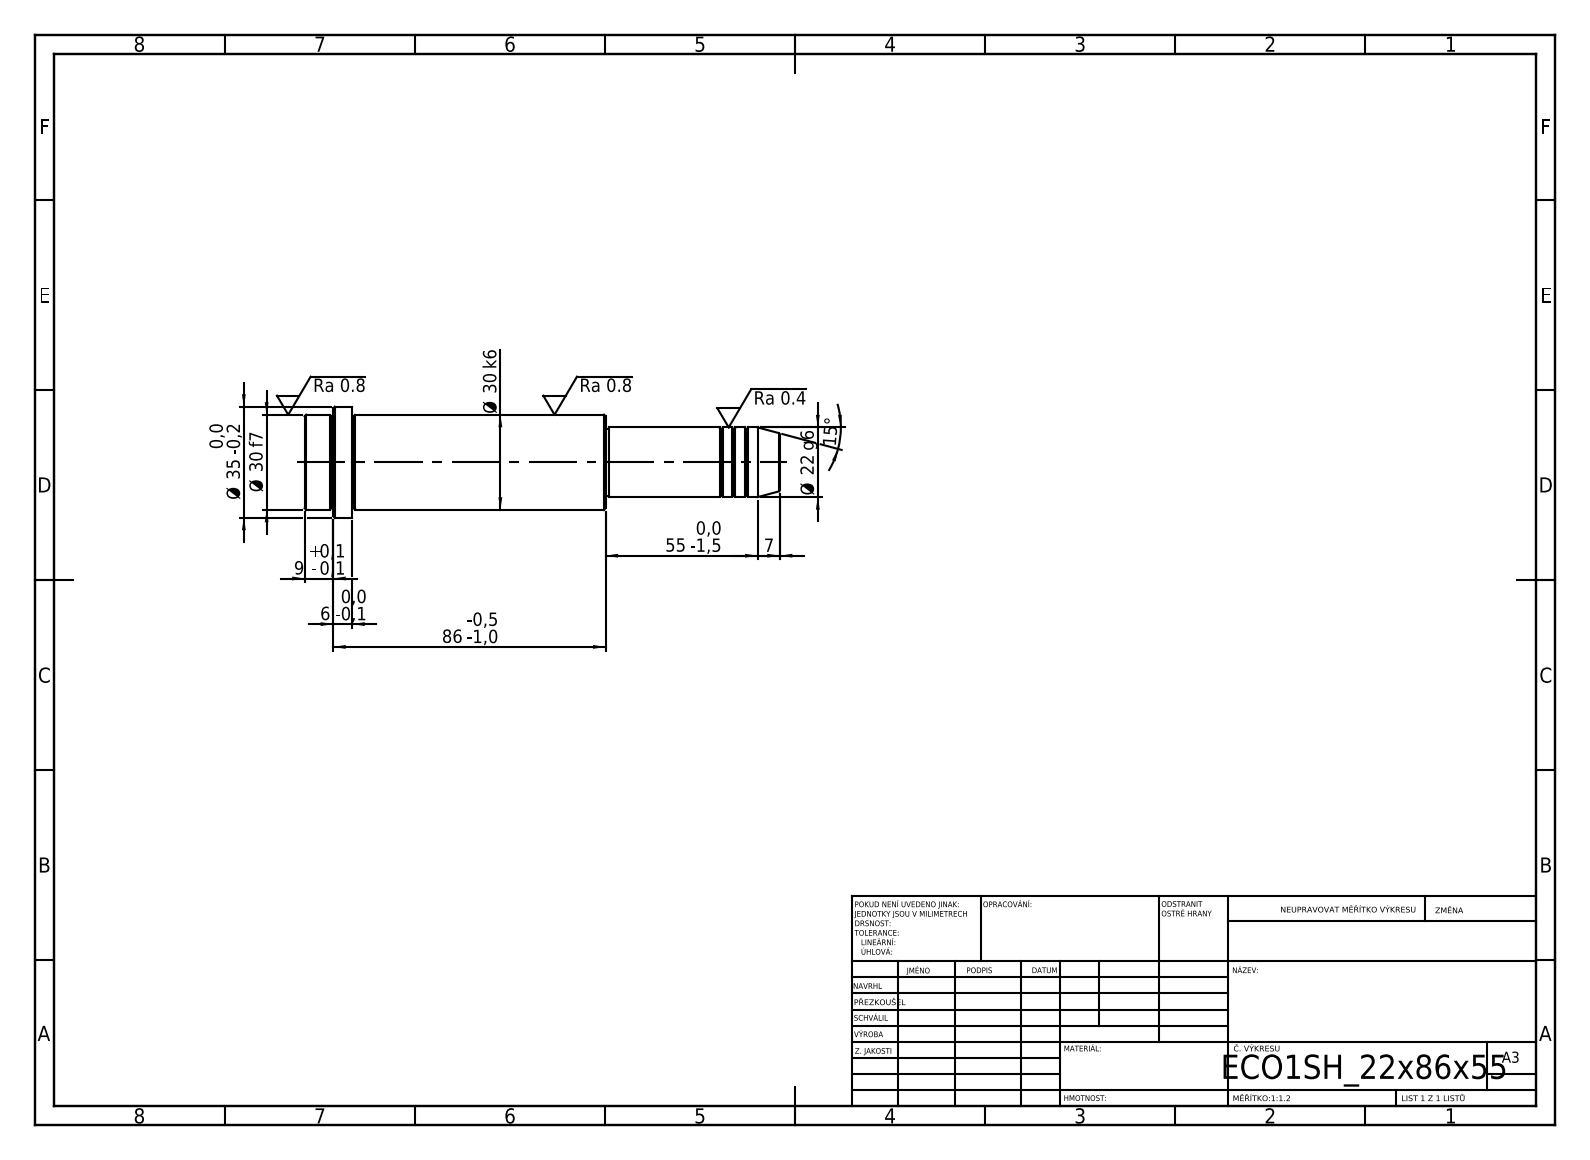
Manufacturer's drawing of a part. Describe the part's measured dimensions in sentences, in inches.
Its 3-D file was written by "SolidWorks 2019 (CONFIG_CONTROL_DESIGN)". It is 1 solid with 52 faces: 6 planar, 16 cylindrical and 30 other. Overall it measures 5.906 by 1.378 by 1.378 inches. Its volume is 5.427 cubic inches and its surface area 22.95 square inches. Round bosses or shafts: 1 of diameter 1.378, 1 of diameter 1.181, 1 of diameter 0.866, 1 of diameter 0.827. The main face-to-face distances are 3.74, 3.15, 0.591, 2.165, 5.315, 5.906, 5.551, 3.386, 0.236, 0.354.
